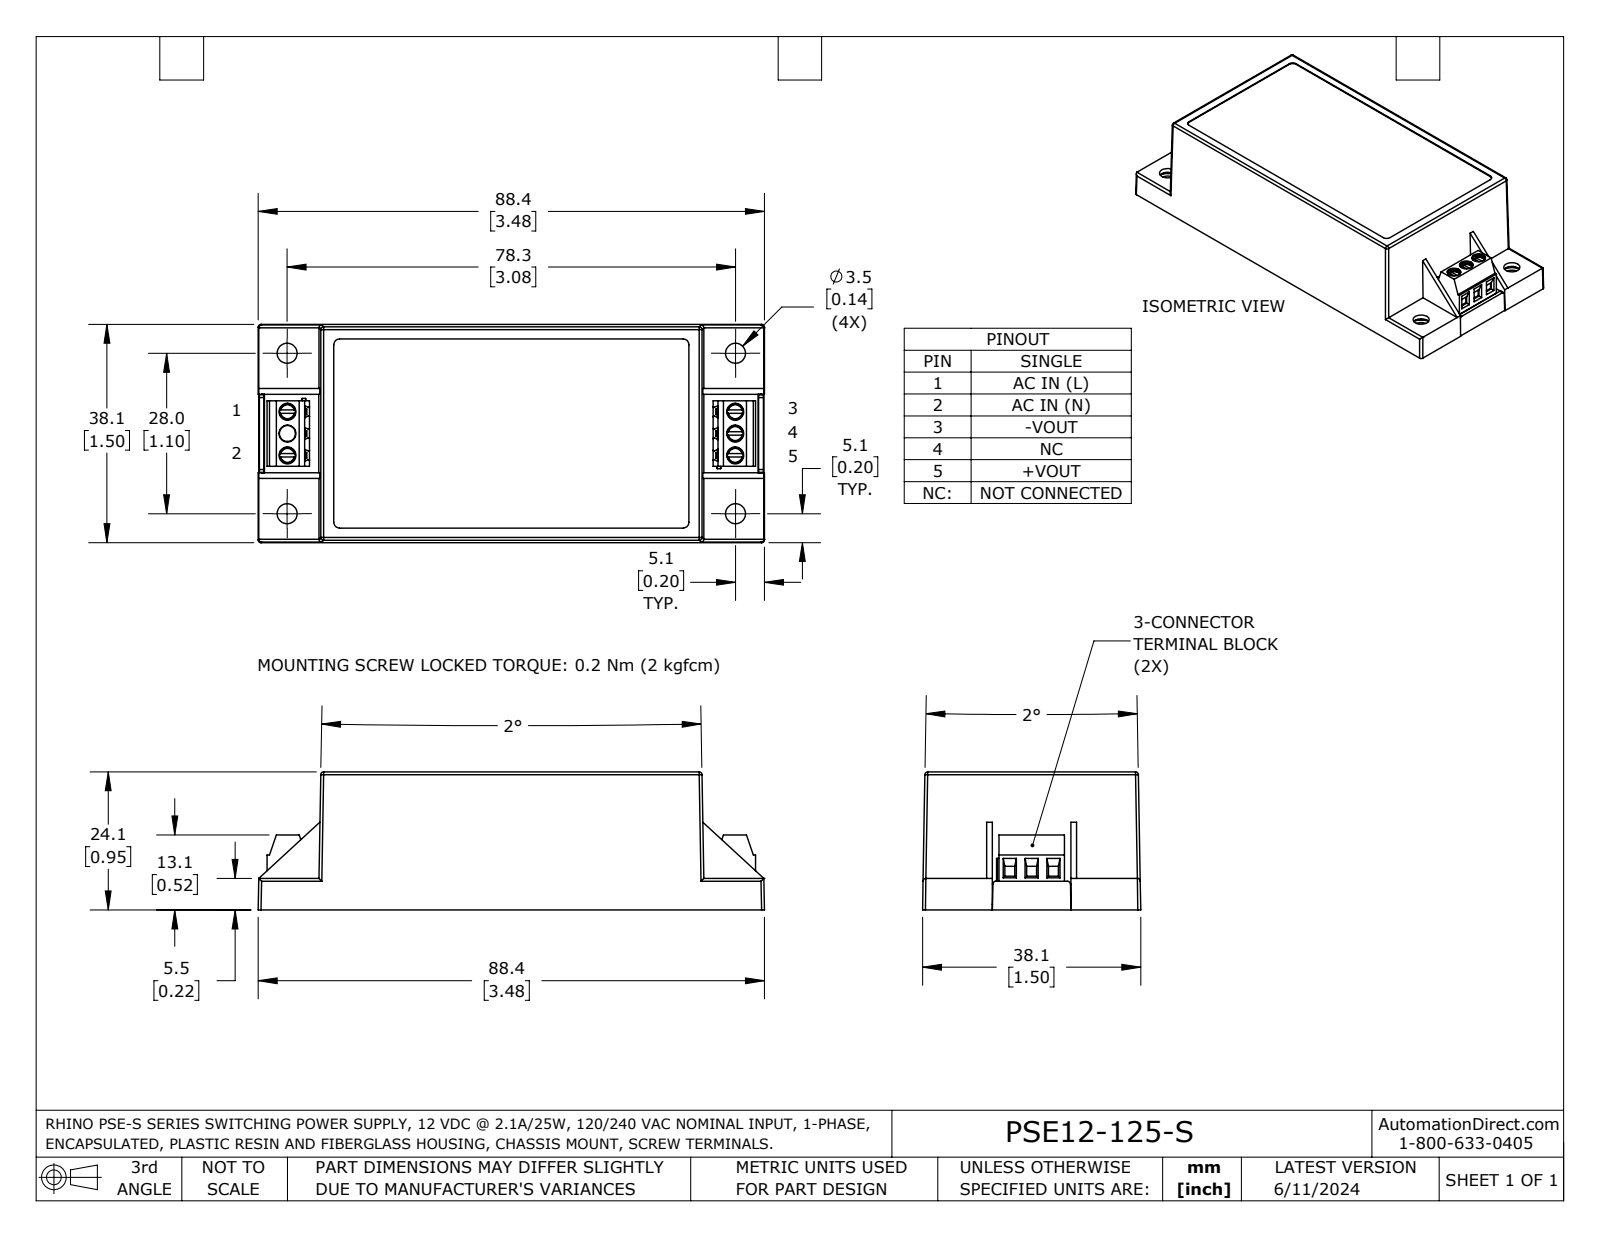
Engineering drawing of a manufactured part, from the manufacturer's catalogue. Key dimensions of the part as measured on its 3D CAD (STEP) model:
Part name (STEP PRODUCT): PSE12-125-S
STEP written by: SolidWorks 2023 (AUTOMOTIVE_DESIGN)
Units: inches
Bodies: 4 solids, 488 faces (328 planar, 126 cylindrical, 34 other)
Overall size (bounding box): 3.48 × 1.5 × 0.968
Volume: 0.709 in³ · Surface area: 38.52 in²
Round holes (diameter × count): ⌀0.116 ×6, ⌀0.138 ×4, ⌀0.11 ×1
Partial cylindrical surfaces — rounded edges, fillets, slot ends (radius × count): R0.009 ×18, R0.02 ×18, R0.006 ×12, R0.004 ×8, R0.008 ×4, R0.01 ×4, R0.039 ×4, R0.079 ×4
Main face-to-face distances: 0.039, 0.902, 0.862, 0.941, 1.422, 0.178, 0.724, 2.575, 0.138, 0.909
Hole centre spacings: 0.15, 0.401, 0.551, 0.701, 3.082, 3.107, 3.13, 3.159
